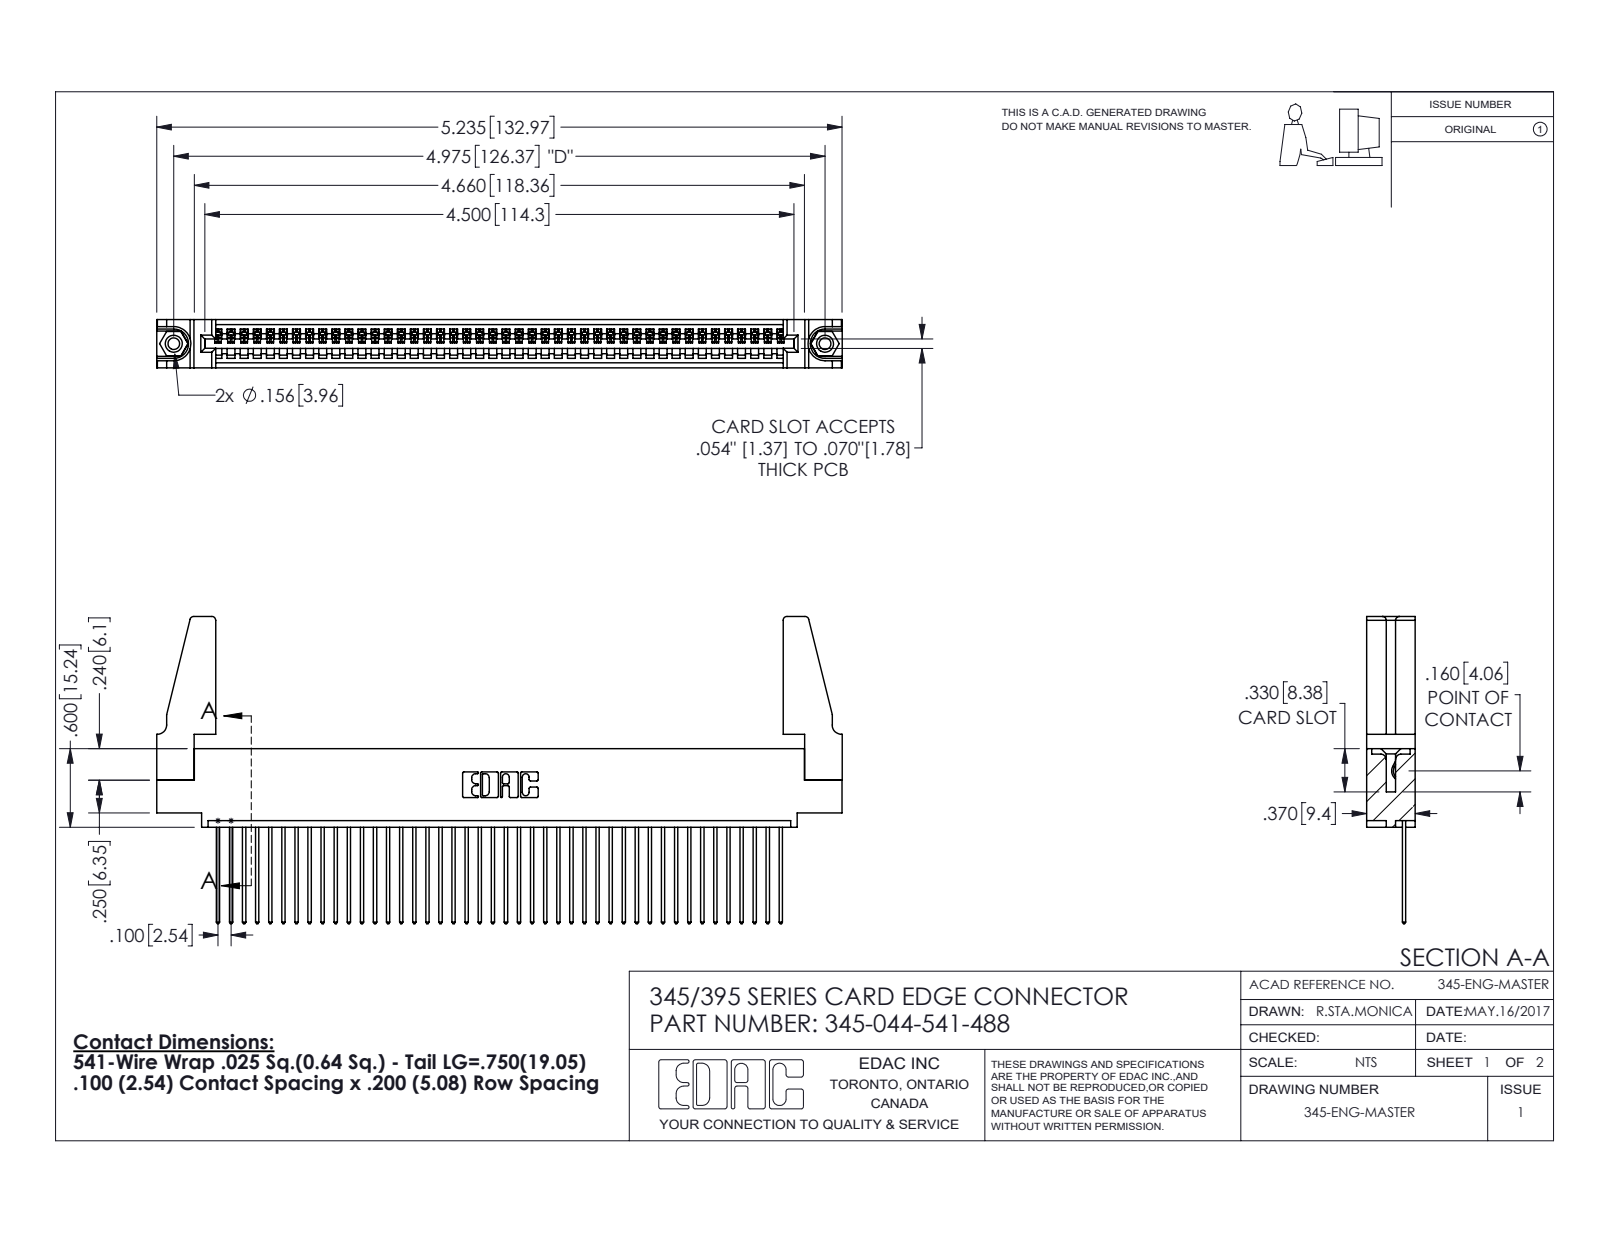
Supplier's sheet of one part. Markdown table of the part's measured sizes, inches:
| quantity | value |
| --- | --- |
| part name | 345-044-541-488; 345-292-001_345-293-141; 345 Part_0.110 Offset - 0.156 Dia-TH; 345-220-078_345-220-088 (+1 more) |
| STEP written by | SolidWorks 2016 (CONFIG_CONTROL_DESIGN) |
| units | inches |
| bodies | 49 solids, 2806 faces (1916 planar, 874 cylindrical, 16 other) |
| overall size | 5.236 × 2.347 × 0.37 |
| volume | 0.975 in³ |
| surface area | 32.54 in² |
| round holes (diameter × count) | 0.089 × 2, 0.125 × 2, 0.156 × 2, 0.064 × 1 |
| round bosses / shafts (diameter × count) | 0.155 × 2 |
| partial cylindrical surfaces (radius × count) | 0.006 × 88, 0.01 × 88, 0.01 × 22, 0.03 × 8, 0.007 × 6, 0.031 × 6, 0.026 × 3, 0.031 × 2 |
| main face-to-face distances | 0.072, 0.298, 0.37, 0.098, 0.272, 0.025, 0.2, 0.225, 0.149, 0.072 |
| hole center spacings | 0.27, 4.739, 4.975 |
